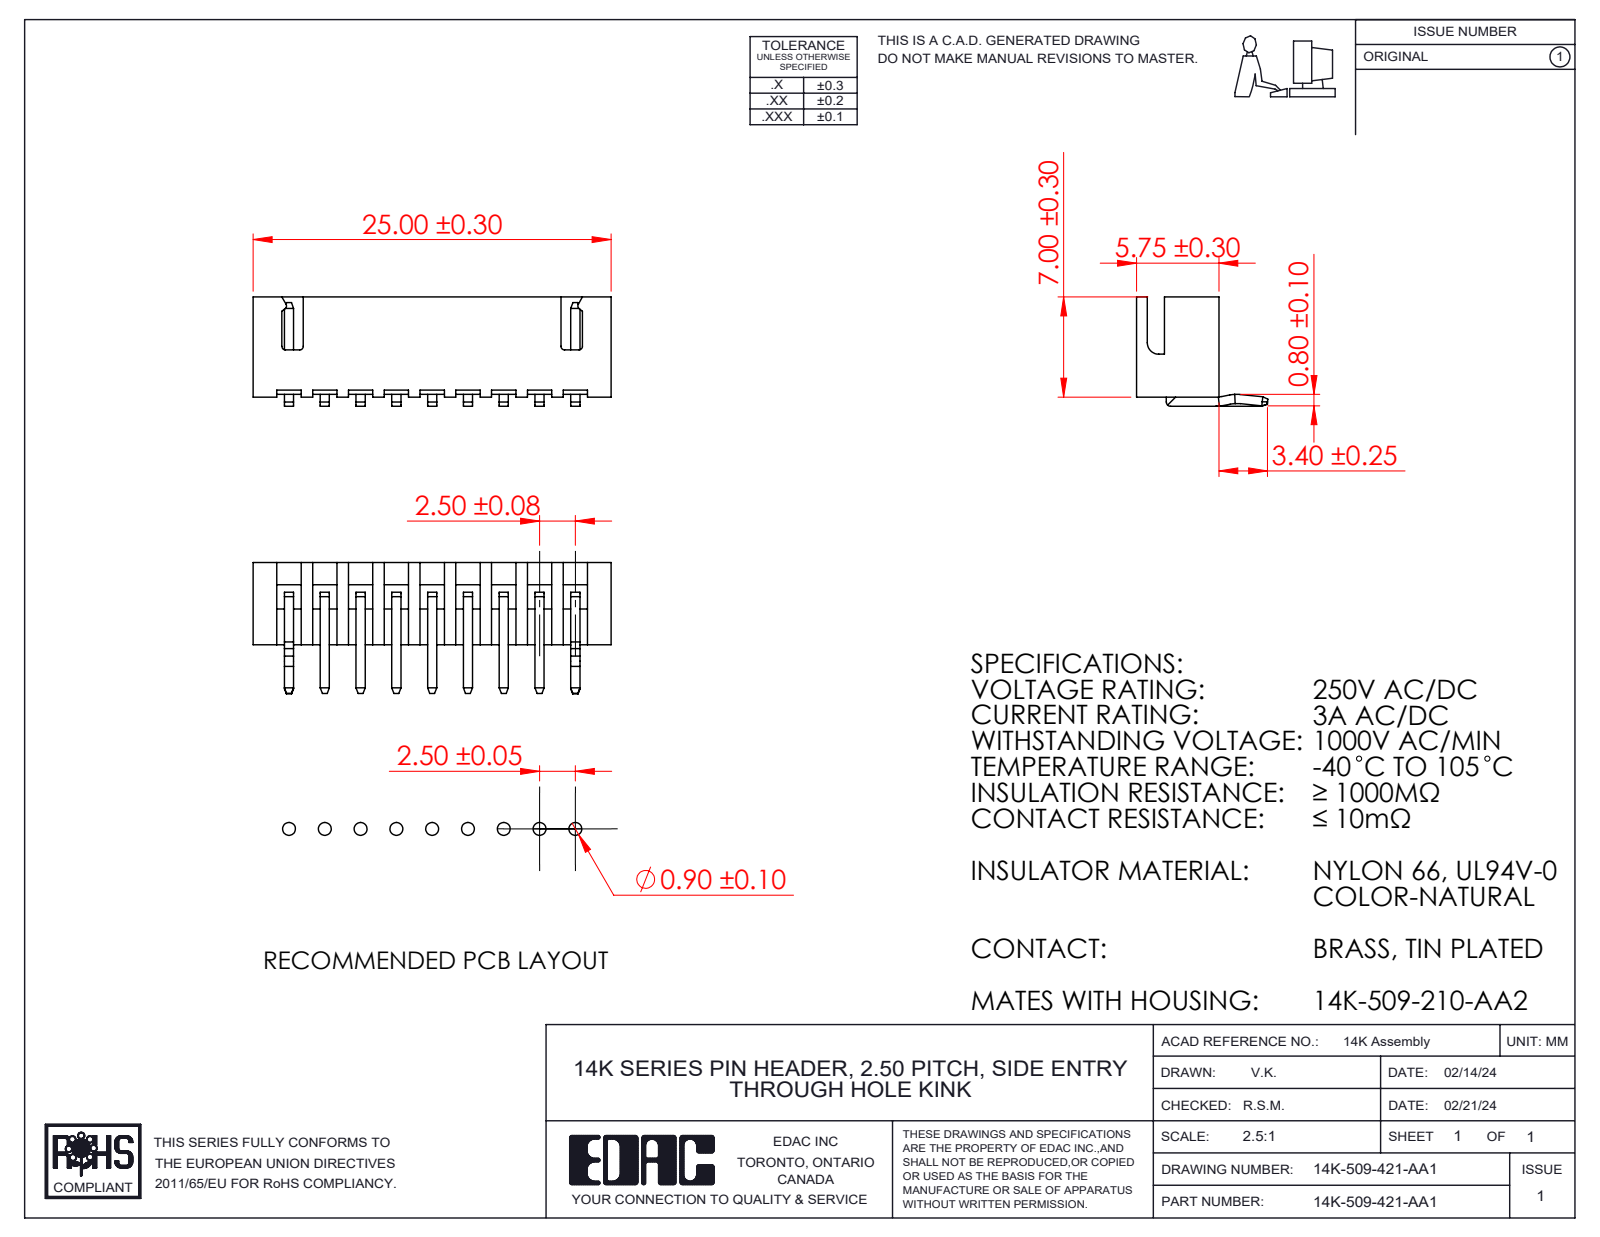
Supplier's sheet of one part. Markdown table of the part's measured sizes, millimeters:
| quantity | value |
| --- | --- |
| part name | 14K Series Pin Header Insulator_509; 14K Series Pin_16; 14K Series Pin_21; 14K-509-421-AA1 |
| STEP written by | SolidWorks 2023 (CONFIG_CONTROL_DESIGN) |
| units | millimeters |
| bodies | 10 solids, 356 faces (317 planar, 39 cylindrical, 0 other) |
| overall size | 25 × 9.17 × 7.64 |
| volume | 481 mm³ |
| surface area | 1 359 mm² |
| partial cylindrical surfaces (radius × count) | 0.25 × 6, 2.5 × 4, 0.3 × 2, 0.8 × 1 |
| main face-to-face distances | 5, 0.76, 5.76, 0.64, 2.5, 4.24, 7.5, 10, 12.5, 3.14 |
